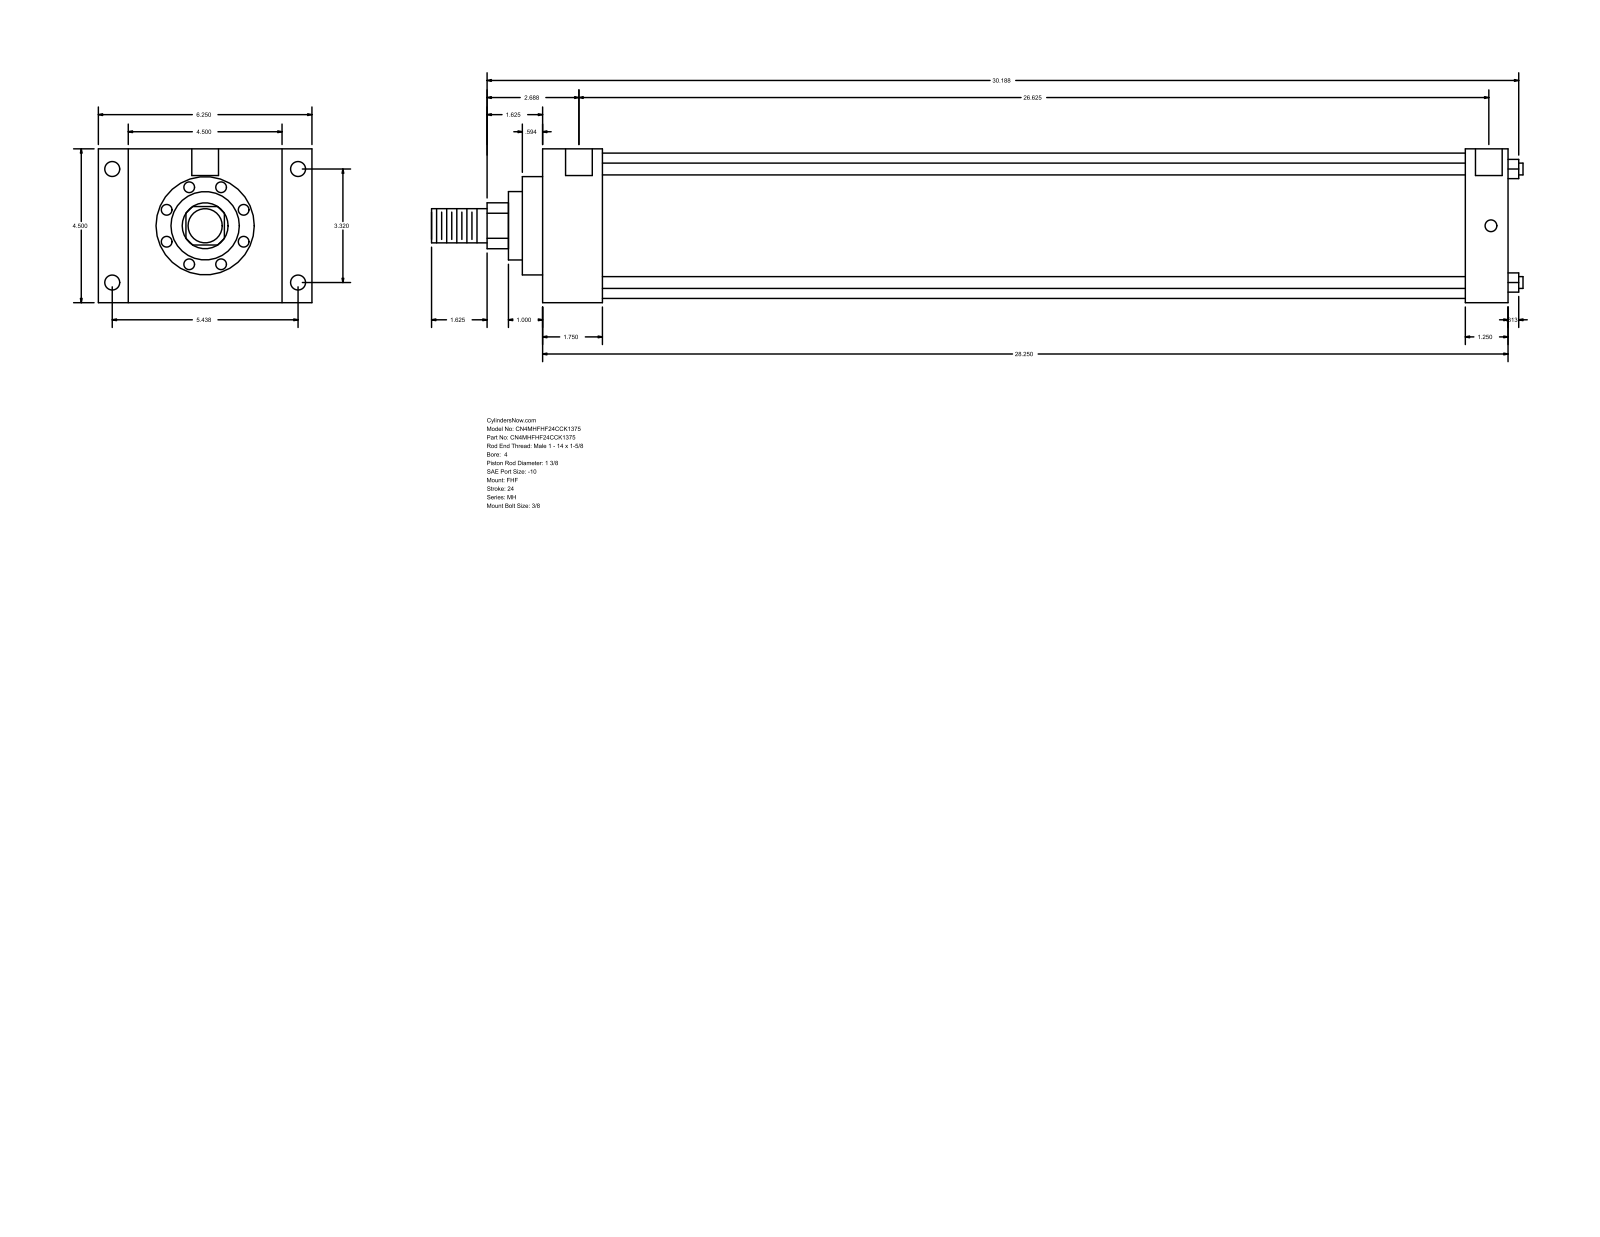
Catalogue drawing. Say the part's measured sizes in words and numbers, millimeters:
The part is named "MH_FHF__0400_1.375". Its 3-D file was written by "GSSL Pune (CONFIG_CONTROL_DESIGN)". It is 0 solids with 90 faces: 61 planar, 29 cylindrical and 0 other. Overall it measures 811.21 by 158.75 by 114.3 millimeters. Round holes: 4 of diameter 8.73, 4 of diameter 11.13, 2 of diameter 19.84. Round bosses or shafts: 4 of diameter 8.76, 1 of diameter 107.95, 1 of diameter 73.03, 1 of diameter 50.8, 1 of diameter 34.92, 1 of diameter 25.4. Partial cylindrical surfaces (rounded edges, fillets, slot ends): 1 of radius 17.06. The main face-to-face distances are 114.3, 717.56, 44.45, 673.11, 22.23, 136.53, 158.76, 685.81, 641.36, 31.75. The hole center spacings are 84.32, 138.12, 161.82, 679.45, 1.58, 1.59, 676.28, 677.86.
